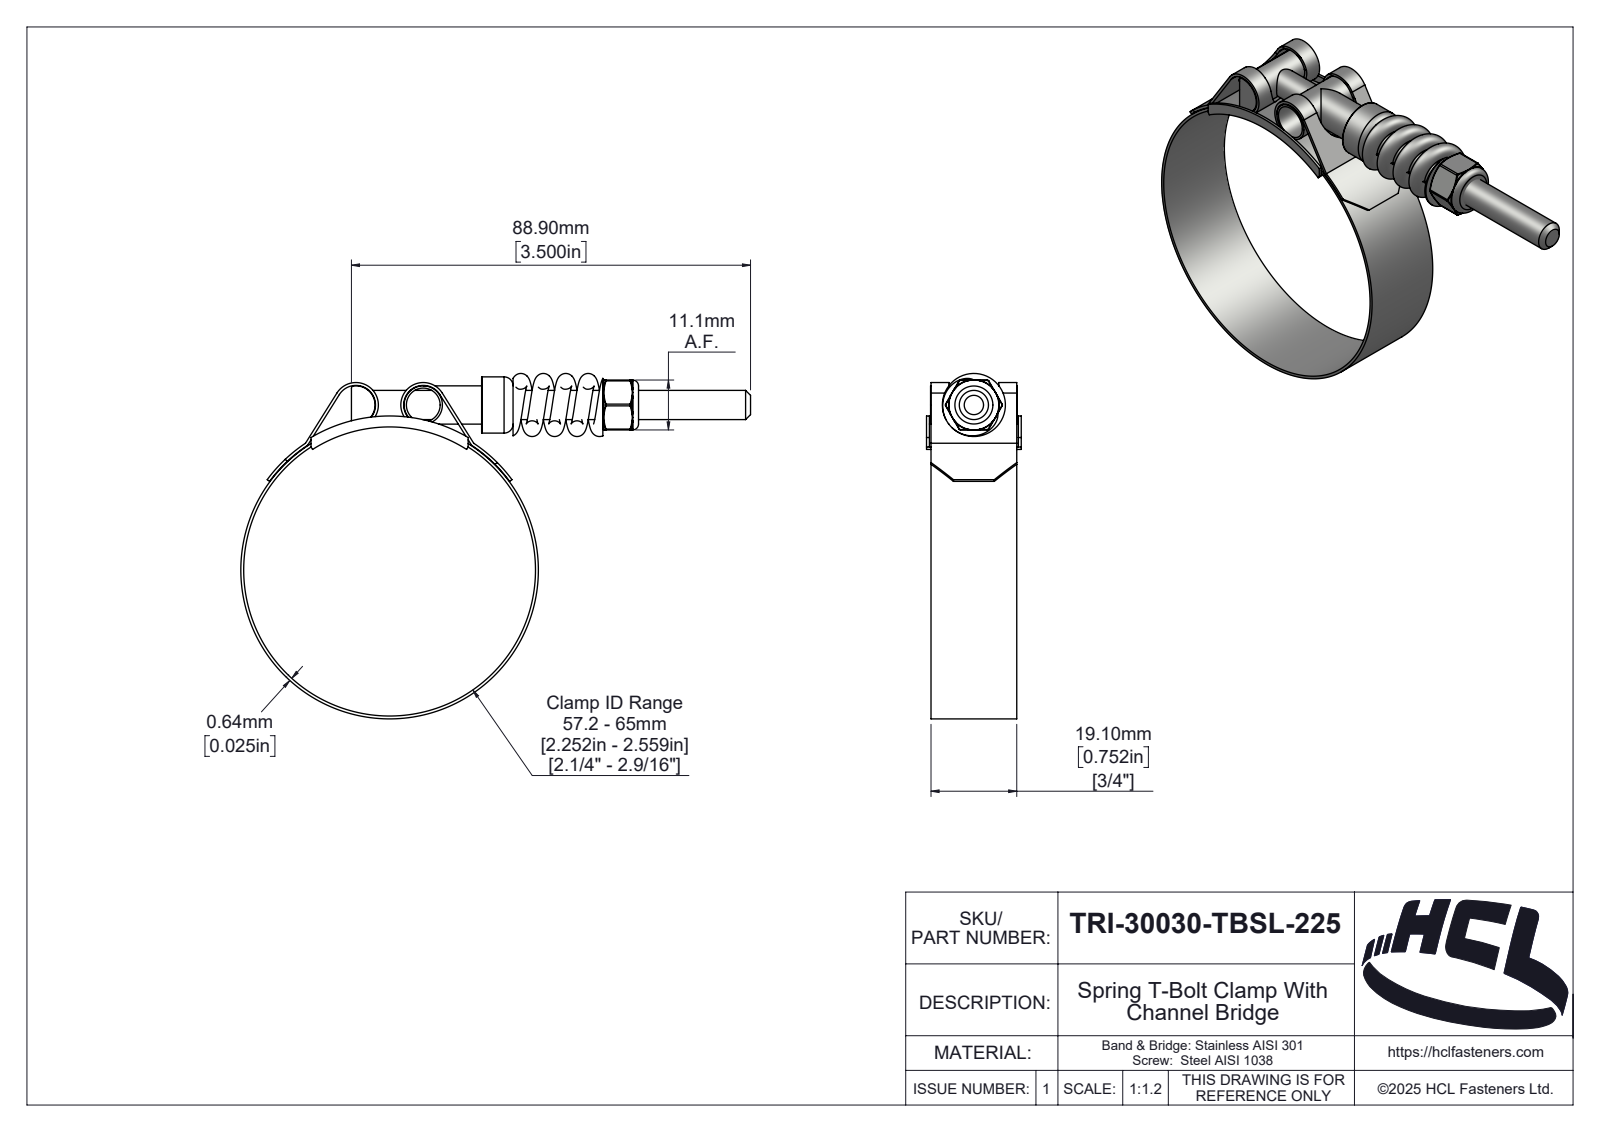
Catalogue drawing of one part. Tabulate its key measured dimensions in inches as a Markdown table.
| quantity | value |
| --- | --- |
| part name | TRI-30030-TBSL-225 |
| STEP written by | SolidWorks 2025 (AUTOMOTIVE_DESIGN) |
| units | inches |
| bodies | 7 solids, 340 faces (52 planar, 126 cylindrical, 162 other) |
| overall size | 4.509 × 3.028 × 0.831 |
| volume | 0.616 in³ |
| surface area | 28.73 in² |
| round holes (diameter × count) | 0.213 × 1, 0.25 × 1, 0.256 × 1, 0.296 × 1, 2.559 × 1 |
| round bosses / shafts (diameter × count) | 0.335 × 2, 2.609 × 1, 0.493 × 1 |
| partial cylindrical surfaces (radius × count) | 0.015 × 6, 0.02 × 2, 0.172 × 2, 0.197 × 2, 0.22 × 2, 0.023 × 1, 0.095 × 1, 0.119 × 1 |
| main face-to-face distances | 0.025, 0.039, 0.791, 0.752, 0.806, 0.014, 0.766, 2.205, 0.437, 0.035 |
| hole center spacings | 1.476 |
